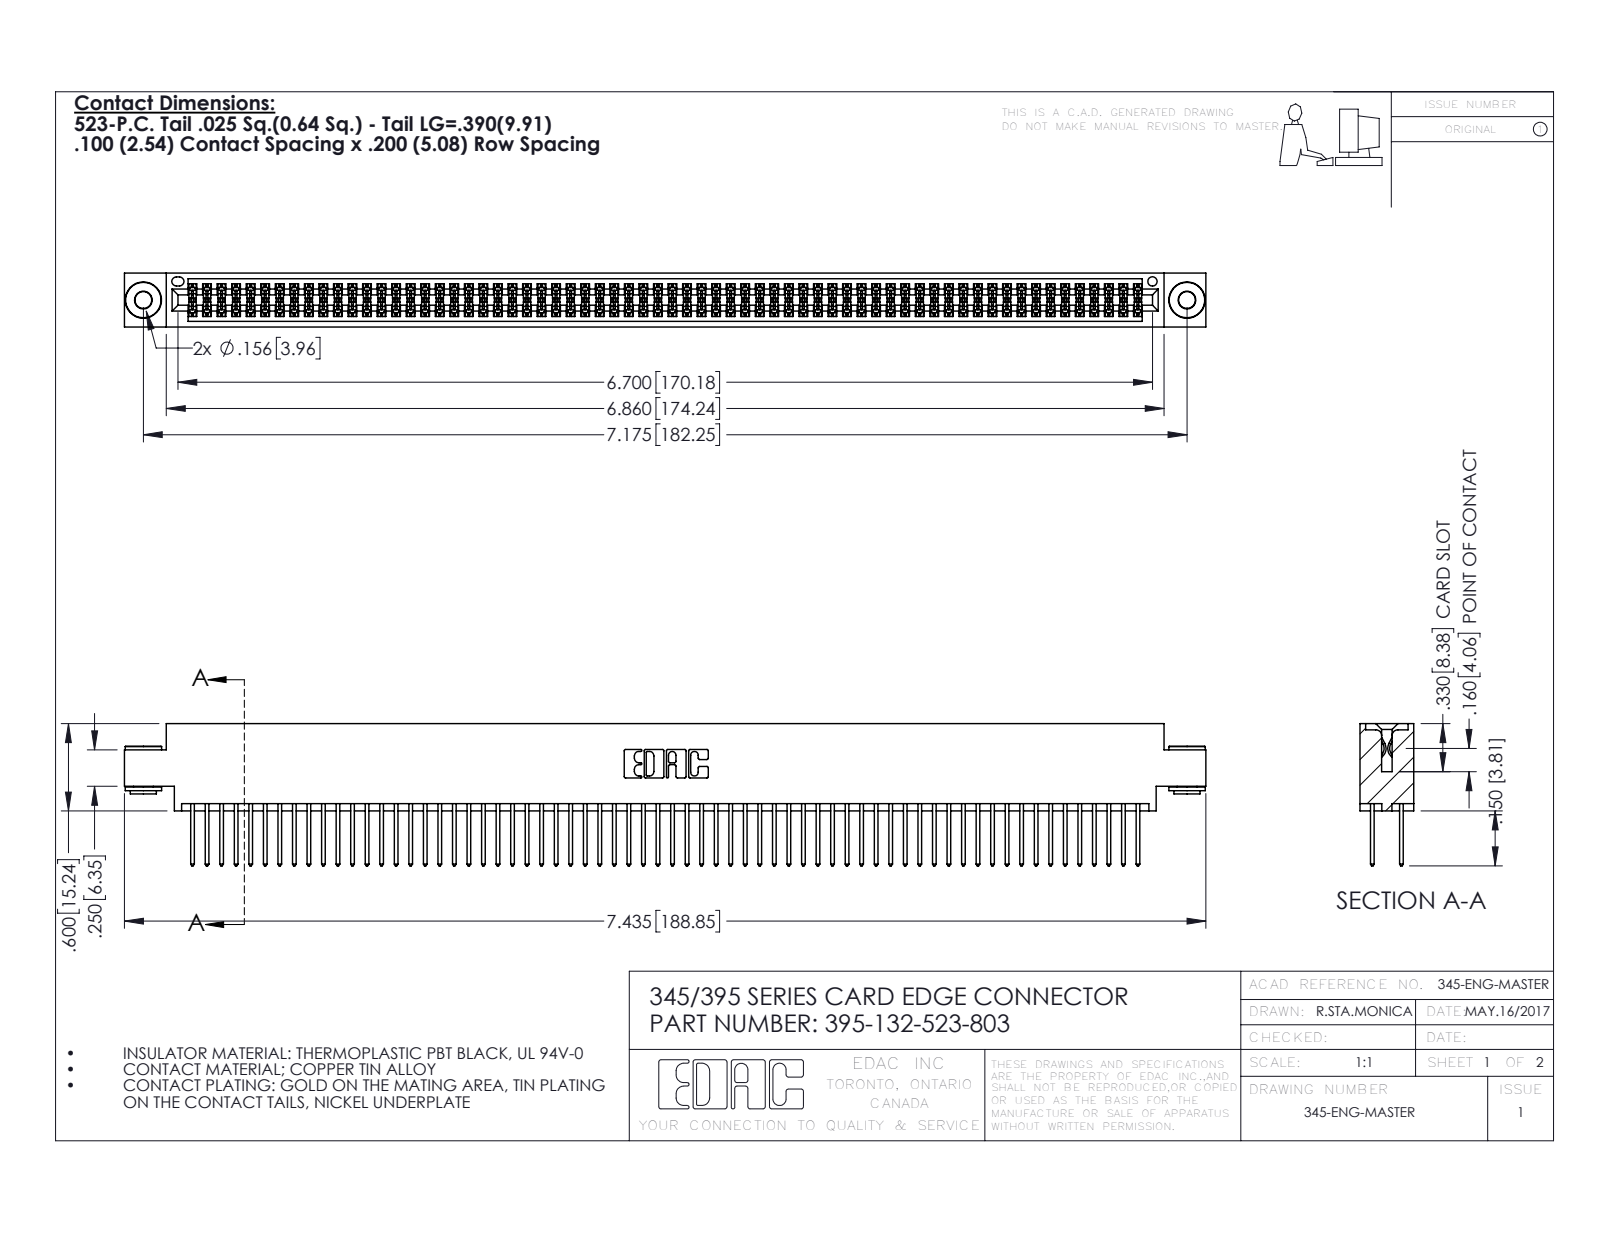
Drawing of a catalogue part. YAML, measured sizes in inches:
part_name: "345-292-001_345-293-123; 345-250-002_345-250-002-102; 345 Part_0.170 Offset - 0.156 Dia-TH; 395-132-523-803"
step_written_by: "SolidWorks 2016 (CONFIG_CONTROL_DESIGN)"
units: inches
bodies: {solids: 135, faces: 6768, planar: 4450, cylindrical: 2310, other: 8}
overall_size: [7.435, 0.977, 0.37]
volume: 1.144
surface_area: 46.09
round_holes:
  - {diameter: 0.116, count: 2}
  - {diameter: 0.156, count: 2}
  - {diameter: 0.064, count: 1}
round_bosses_or_shafts:
  - {diameter: 0.25, count: 2}
  - {diameter: 0.18, count: 2}
  - {diameter: 0.136, count: 2}
partial_cylinders:
  - {radius: 0.006, count: 198}
  - {radius: 0.01, count: 132}
  - {radius: 0.01, count: 22}
  - {radius: 0.007, count: 6}
  - {radius: 0.031, count: 6}
  - {radius: 0.026, count: 3}
  - {radius: 0.014, count: 2}
  - {radius: 0.019, count: 2}
face_to_face_distances: [0.072, 0.298, 0.2, 0.098, 0.272, 0.025, 0.37, 0.225, 0.175, 0.149]
hole_center_spacings: [0.27, 6.939, 7.175]
